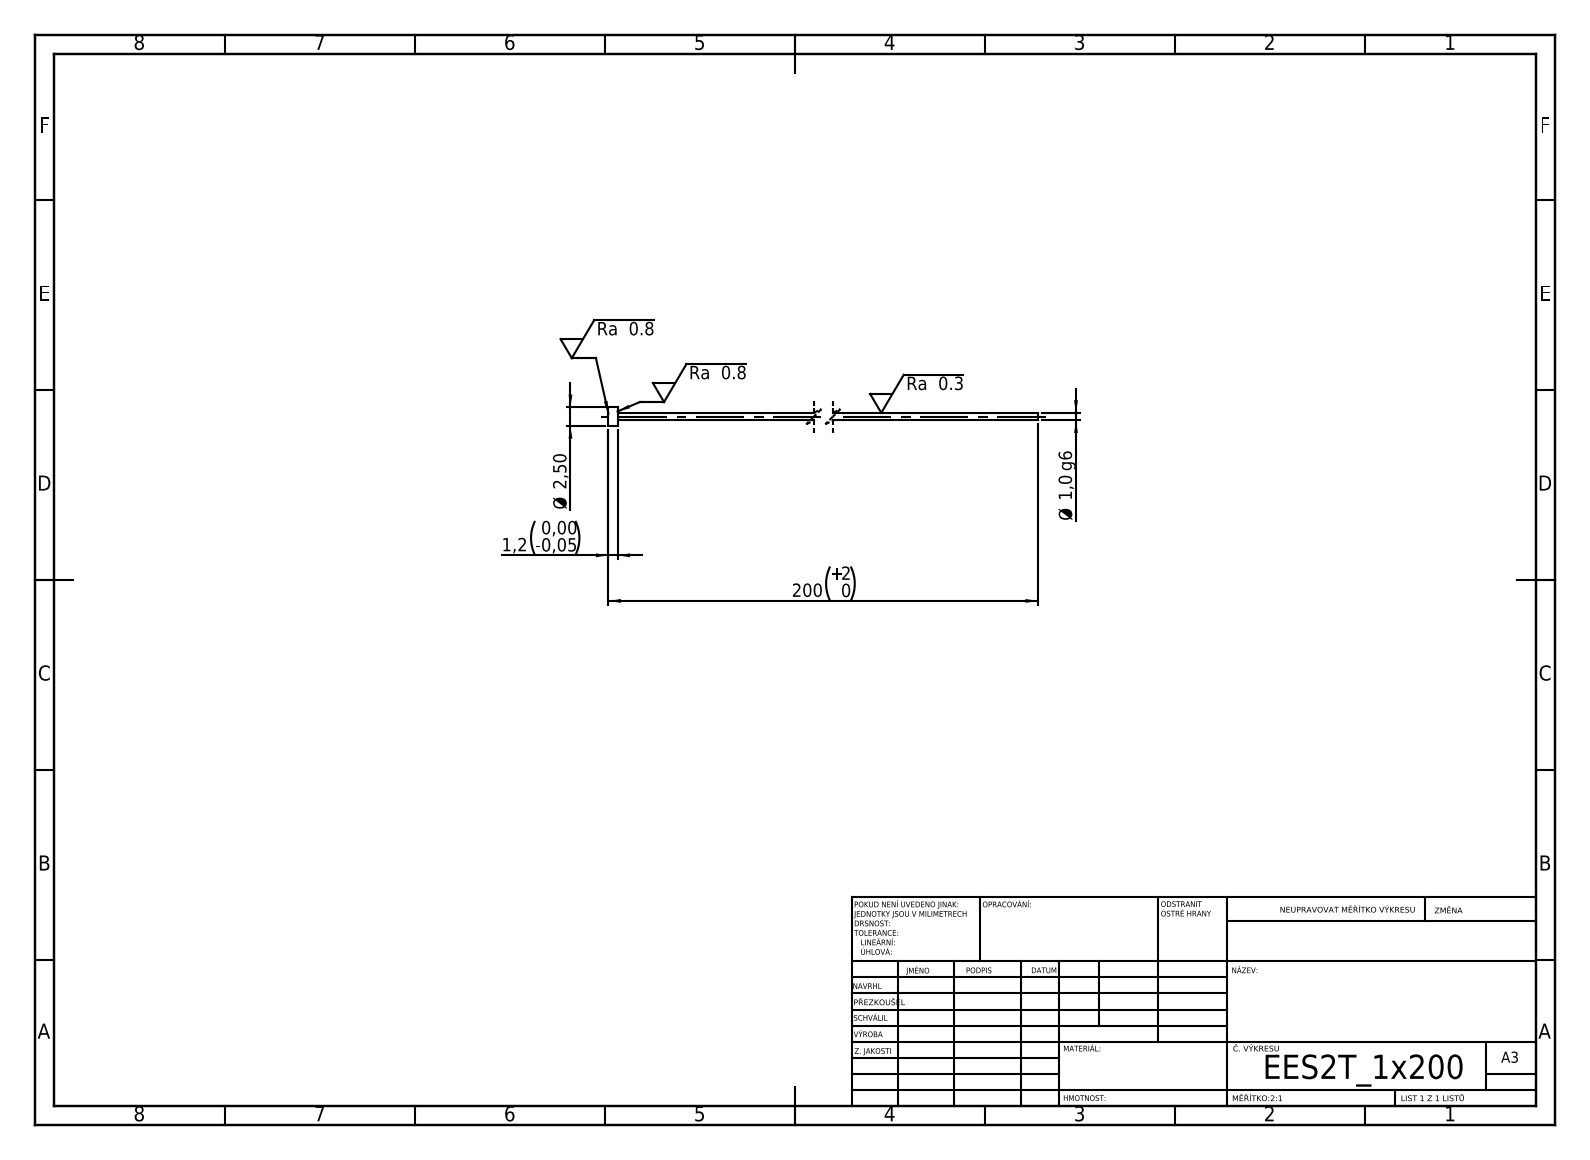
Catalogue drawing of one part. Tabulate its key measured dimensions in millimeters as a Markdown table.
| quantity | value |
| --- | --- |
| STEP written by | SolidWorks 2019 (CONFIG_CONTROL_DESIGN) |
| units | millimeters |
| bodies | 1 solid, 7 faces (3 planar, 4 cylindrical, 0 other) |
| overall size | 200 × 2.5 × 2.5 |
| volume | 162 mm³ |
| surface area | 644 mm² |
| round bosses / shafts (diameter × count) | 2.5 × 1, 1 × 1 |
| main face-to-face distances | 1.2, 200, 198.8 |
